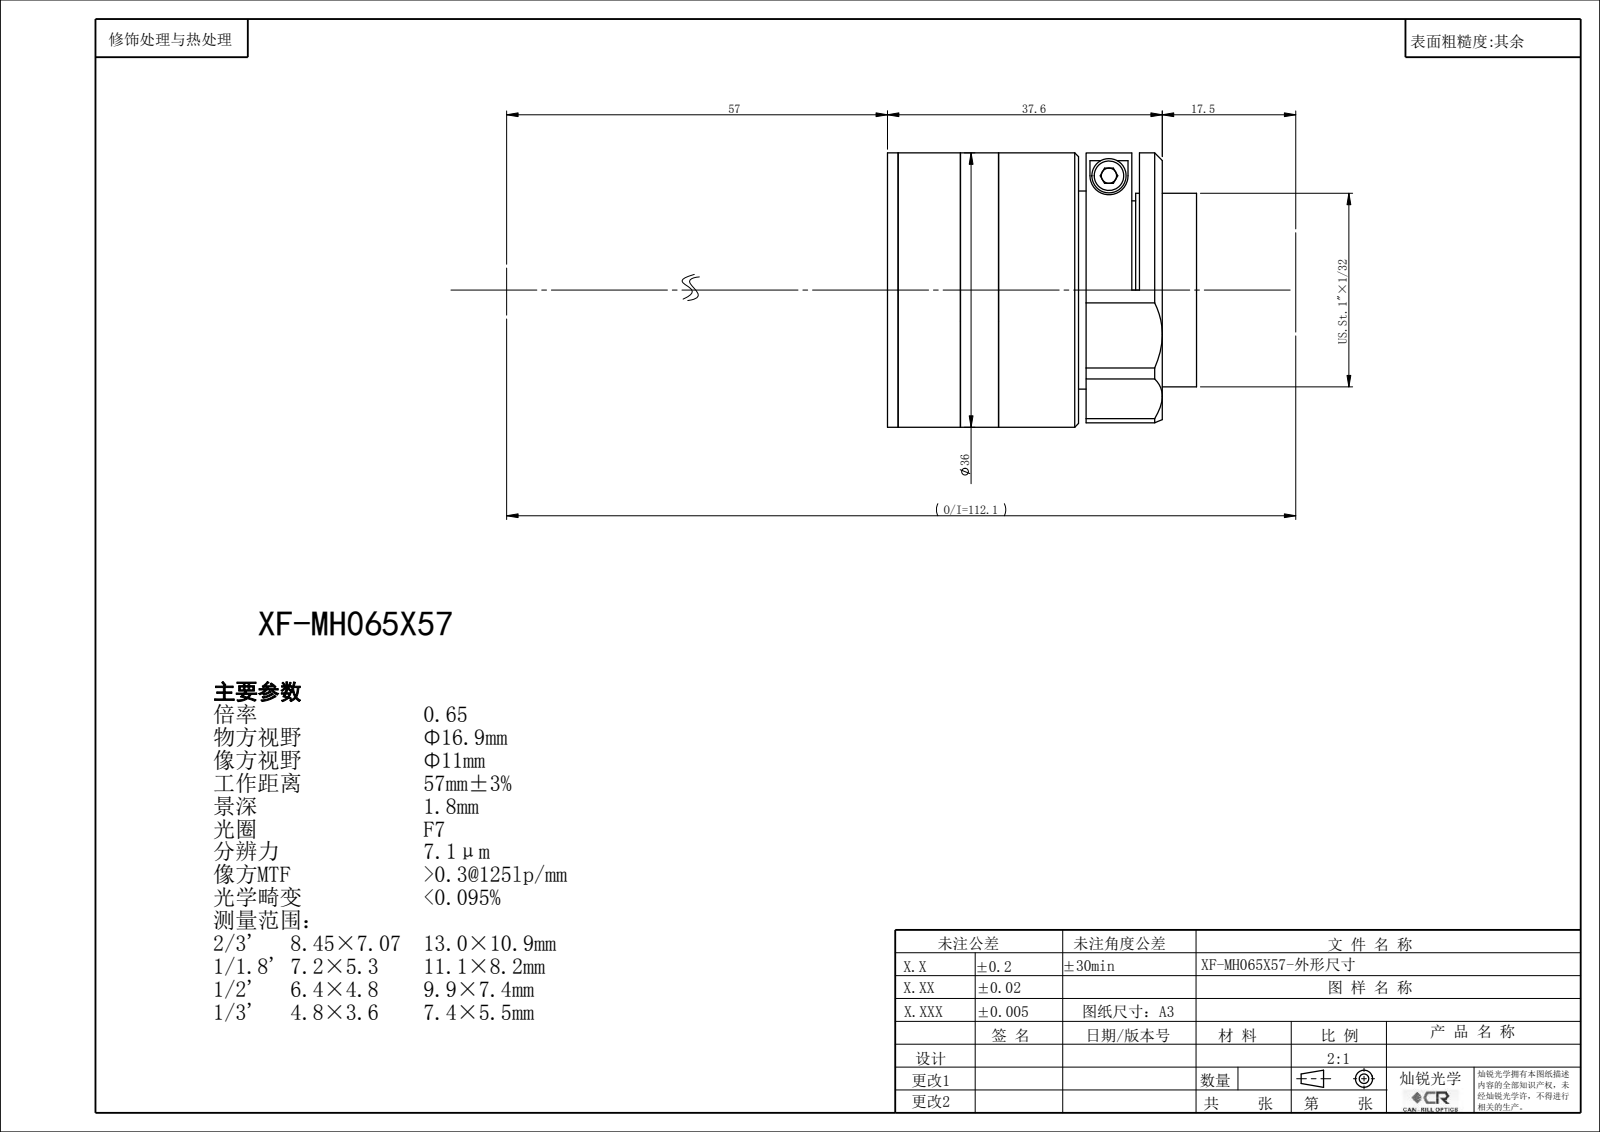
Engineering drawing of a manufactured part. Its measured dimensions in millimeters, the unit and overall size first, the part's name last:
Units: millimetres
Overall size (bounding box): 41.54 × 36 × 36
Round holes (diameter × count): ⌀2.5 ×3, ⌀9 ×1, ⌀13 ×1, ⌀17 ×1, ⌀20 ×1, ⌀21 ×1, ⌀21.5 ×1, ⌀24.9 ×1, ⌀26 ×1
Round bosses / shafts (diameter × count): ⌀36 ×1, ⌀34 ×1, ⌀29 ×1, ⌀25.4 ×1, ⌀24 ×1
Main face-to-face distances: 5.5, 8.19, 9.59, 13.69, 36.14, 27.95, 22.45, 1.4, 15.09, 37.54
Bodies: 0 solids, 92 faces (42 planar, 42 cylindrical, 8 other)
Part name (STEP PRODUCT): XF-MH065X57
STEP written by: SolidWorks 2022 (CONFIG_CONTROL_DESIGN)
